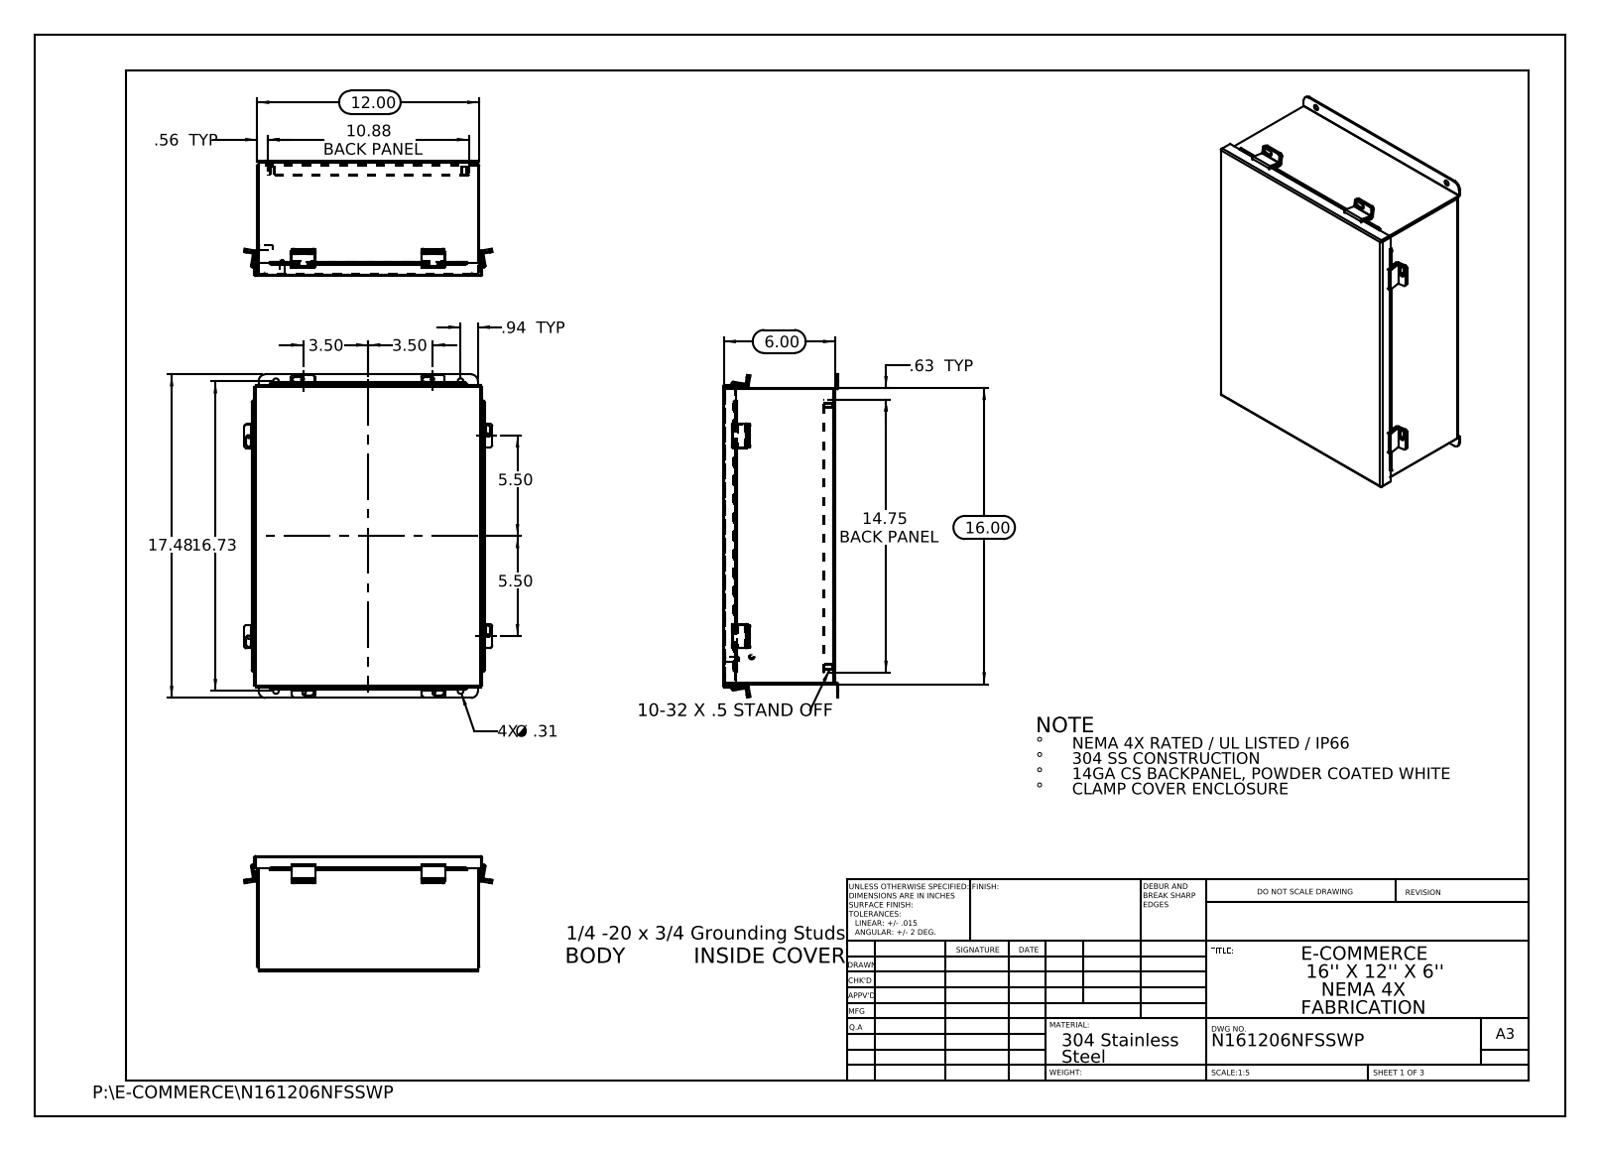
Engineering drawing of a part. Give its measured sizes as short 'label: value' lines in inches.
name: N161206NFSSWP JIC_Standoff; N161206NFSSWP HW-CD-S-25020-034; N161206NFSSWP; N161206NFSSWP JIC Top (+6 more)
written by: SolidWorks 2013 (CONFIG_CONTROL_DESIGN)
unit: in
bodies: 27 solids, 640 faces (420 planar, 200 cylindrical, 20 other)
size: 17.476 × 13.407 × 6.39
volume: 73.88 in³; area: 1 999 in²
holes: 12× ⌀0.25, 4× ⌀0.187, 4× ⌀0.312
bosses: 4× ⌀0.313, 2× ⌀0.315, 2× ⌀0.236
rounds: 30× R0.125, 16× R0.009, 16× R0.133, 12× R0.013, 12× R0.088, 8× R0.083, 8× R0.1, 4× R0.084
face distances: 0.075, 6.128, 6.053, 6.203, 11.925, 0.074, 5.628, 0.575, 0.5, 5.553
hole spacings: 1.315, 10.258, 15.427, 18.48, 7, 9.976, 10.375, 10.85
